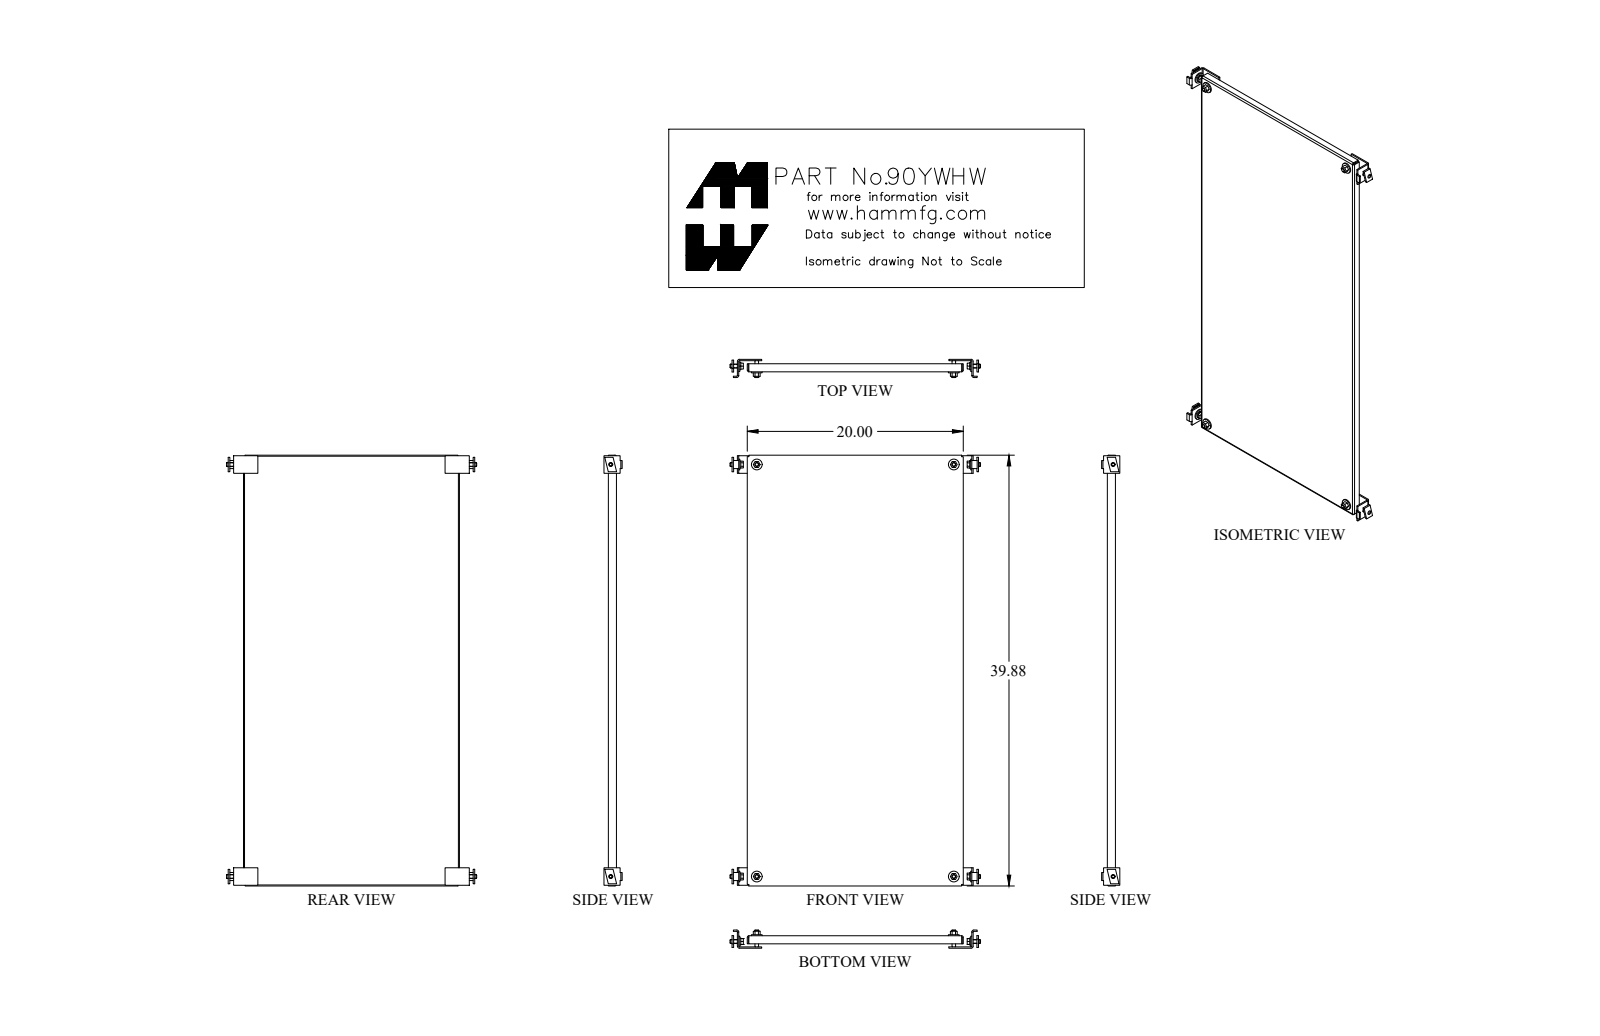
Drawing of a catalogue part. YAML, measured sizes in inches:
part_name: "90YWHW_Default"
step_written_by: "SolidWorks 2018 (CONFIG_CONTROL_DESIGN)"
units: inches
bodies: {solids: 1, faces: 38, planar: 22, cylindrical: 16, other: 0}
overall_size: [39.875, 20, 0.75]
volume: 82.58
surface_area: 1751
round_holes:
  - {diameter: 0.563, count: 4}
partial_cylinders:
  - {radius: 0.048, count: 4}
  - {radius: 0.143, count: 4}
face_to_face_distances: [0.095, 19.905, 19.81, 20, 39.78, 39.875, 39.685, 0.75, 0.655, 0.143]
hole_center_spacings: [18.25, 38.125, 42.268]
